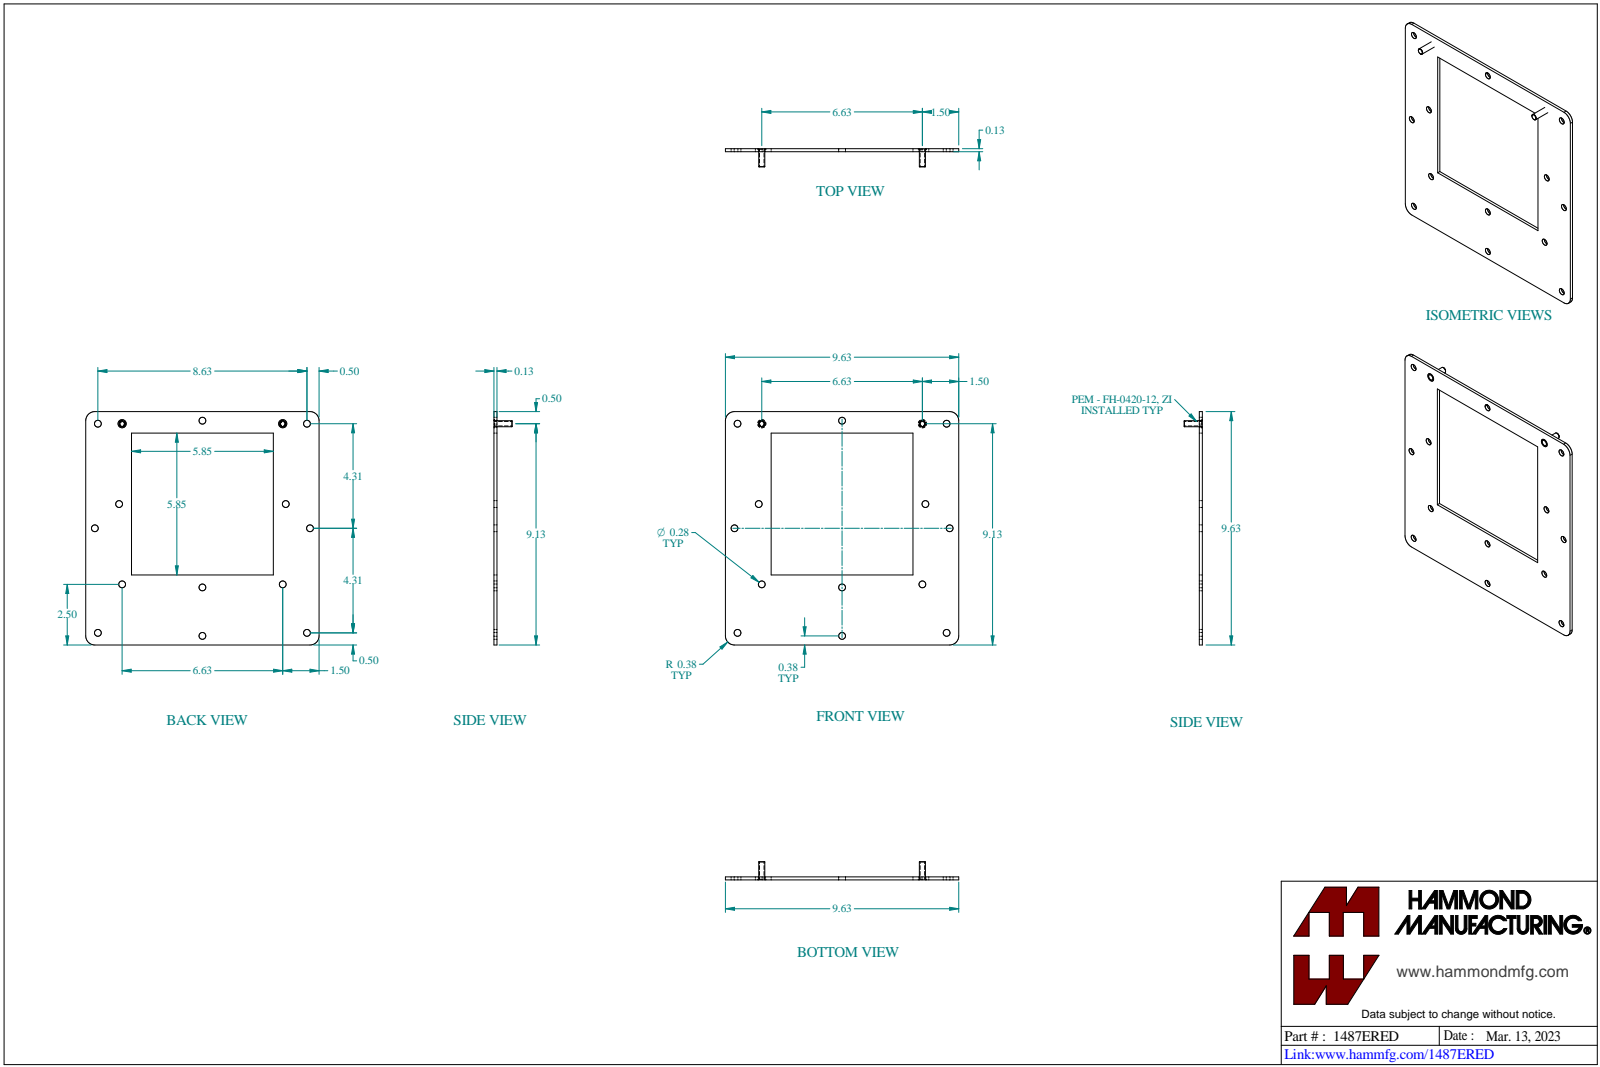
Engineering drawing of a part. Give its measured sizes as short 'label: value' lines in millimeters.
name: 1487ERED
written by: SolidWorks 2023 (CONFIG_CONTROL_DESIGN)
unit: mm
bodies: 5 solids, 131 faces (36 planar, 91 cylindrical, 4 other)
size: 244.5 × 244.5 × 22.2
volume: 224 000 mm³; area: 158 300 mm²
holes: 21× ⌀7.1, 2× ⌀6.3
bosses: 2× ⌀8.6, 2× ⌀6.4
rounds: 8× R6.4, 8× R9.5, 1× R3.6
face distances: 3.2, 6.4, 21.4, 197.7, 25.4, 244.5, 223.1, 219.1, 4, 46.8
hole spacings: 84.2, 191, 214.1, 25.4, 88.8, 109.6, 225.3, 111.8
